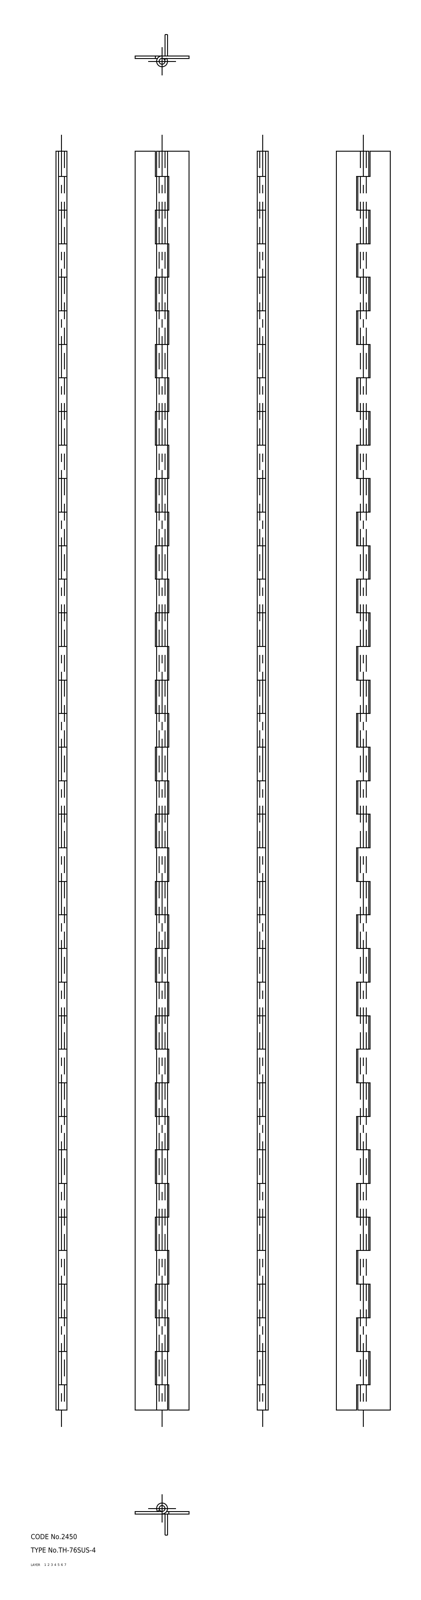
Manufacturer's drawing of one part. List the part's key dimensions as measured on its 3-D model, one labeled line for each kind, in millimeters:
Part name (STEP PRODUCT): shaft; hinge piece_B; hinge piece_A; TH_76SUS_4_15560_36
STEP written by: CADfix (AUTOMOTIVE_DESIGN)
Units: millimetres
Bodies: 3 solids, 240 faces (0 planar, 0 cylindrical, 240 other)
Overall size (bounding box): 750 × 32 × 6.5
Volume: 53 533 mm³ · Surface area: 76 539 mm²
